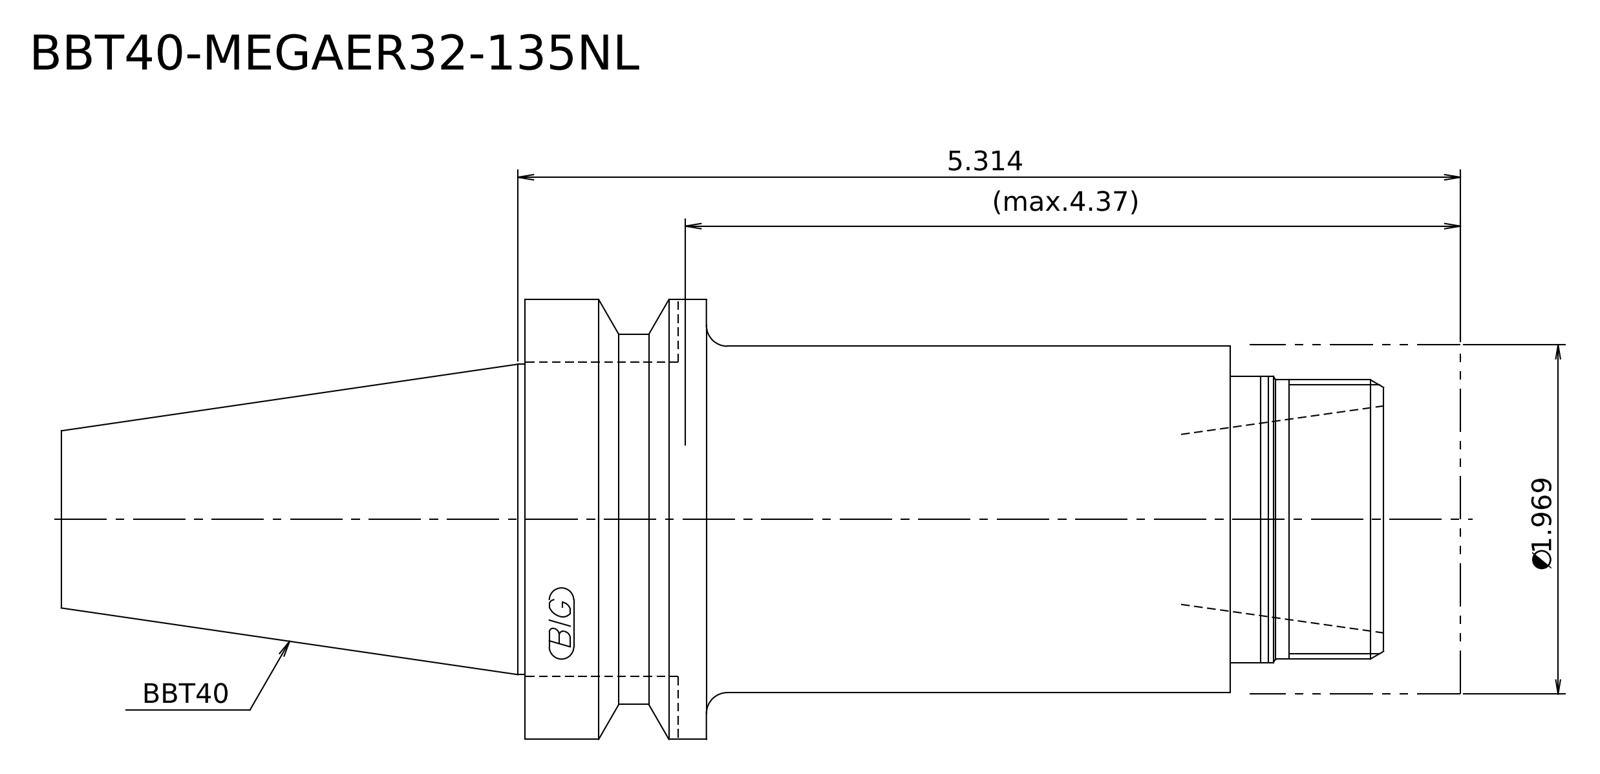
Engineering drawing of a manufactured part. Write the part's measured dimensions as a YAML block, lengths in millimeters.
step_written_by: "Kubotek KeyCreator 2011 V10.0.2 (22737) (automotive_design)"
units: millimeters
bodies: {solids: 2, faces: 21, planar: 6, cylindrical: 8, other: 7}
overall_size: [200.4, 63, 63]
volume: 373010
surface_area: 41297
round_bosses_or_shafts:
  - {diameter: 63, count: 1}
  - {diameter: 53, count: 1}
  - {diameter: 50, count: 1}
  - {diameter: 49.6, count: 1}
  - {diameter: 44.45, count: 1}
  - {diameter: 41, count: 1}
  - {diameter: 40, count: 1}
face_to_face_distances: [30.2, 134, 103.8, 11, 19.2, 123, 33, 22, 2.8, 101]
